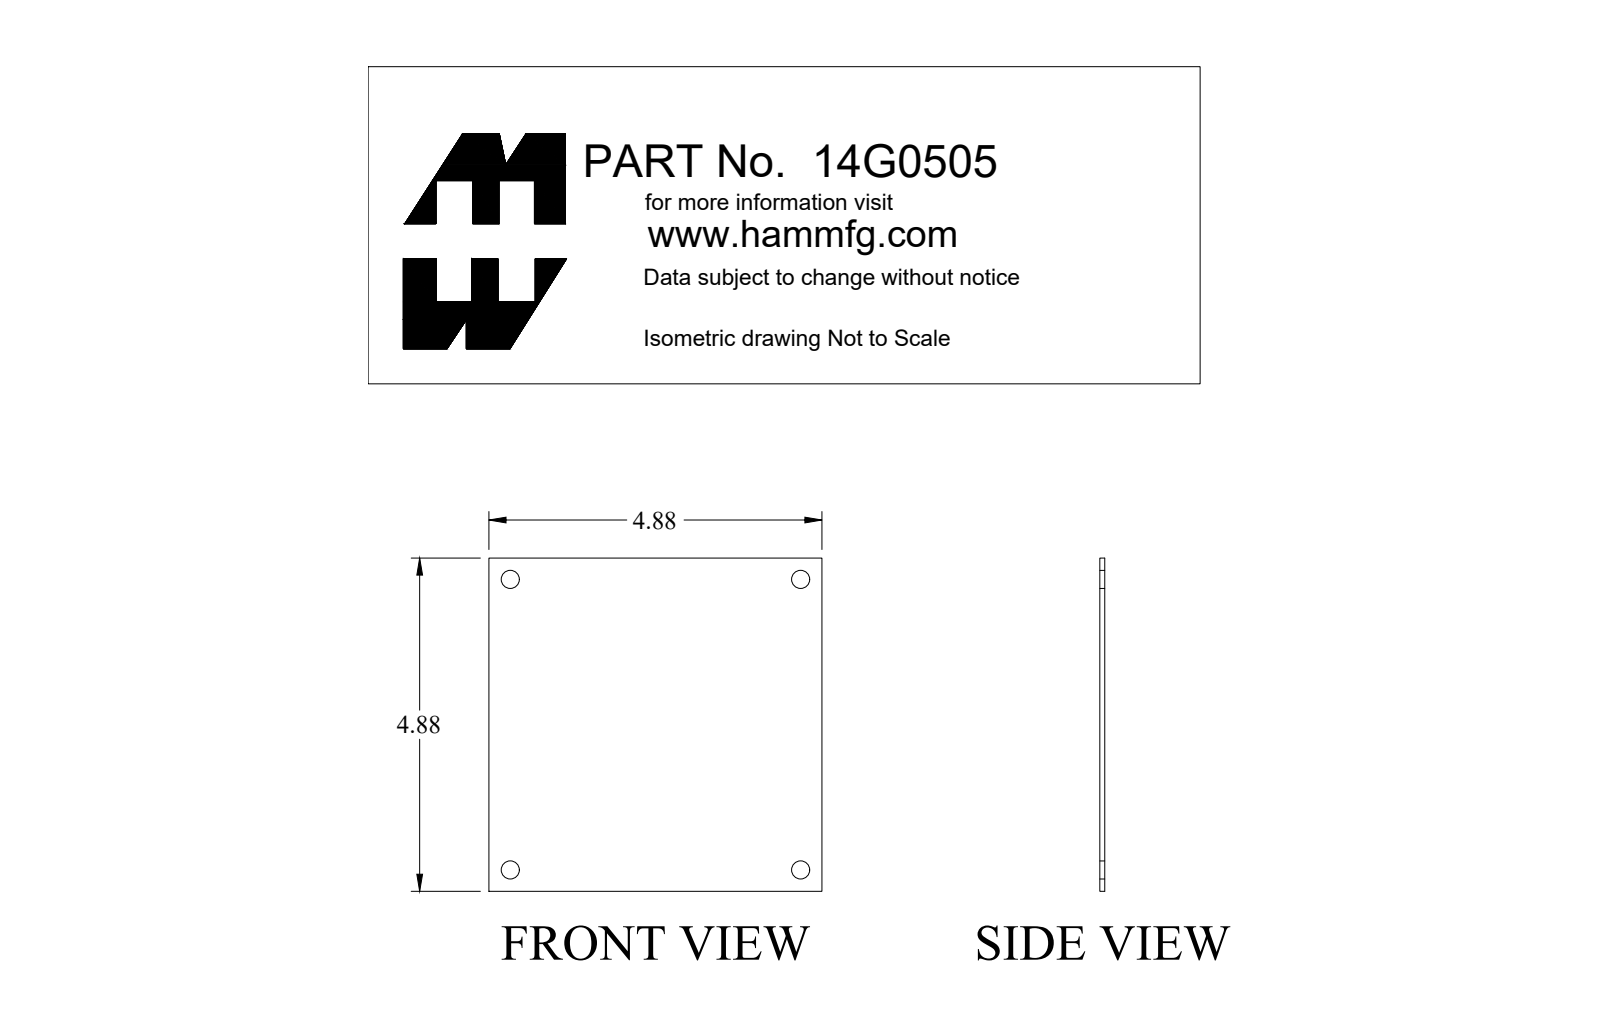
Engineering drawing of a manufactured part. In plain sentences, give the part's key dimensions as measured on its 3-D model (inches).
The part is named "14G0505". Its 3-D file was written by "SolidWorks 2018 (AUTOMOTIVE_DESIGN)". It is 1 solid with 10 faces: 6 planar, 4 cylindrical and 0 other. Overall it measures 4.875 by 4.875 by 0.072 inches. Its volume is 1.695 cubic inches and its surface area 48.73 square inches. Round holes: 4 of diameter 0.265. The main face-to-face distances are 0.072, 4.875. The hole center spacings are 4.25, 6.01.
